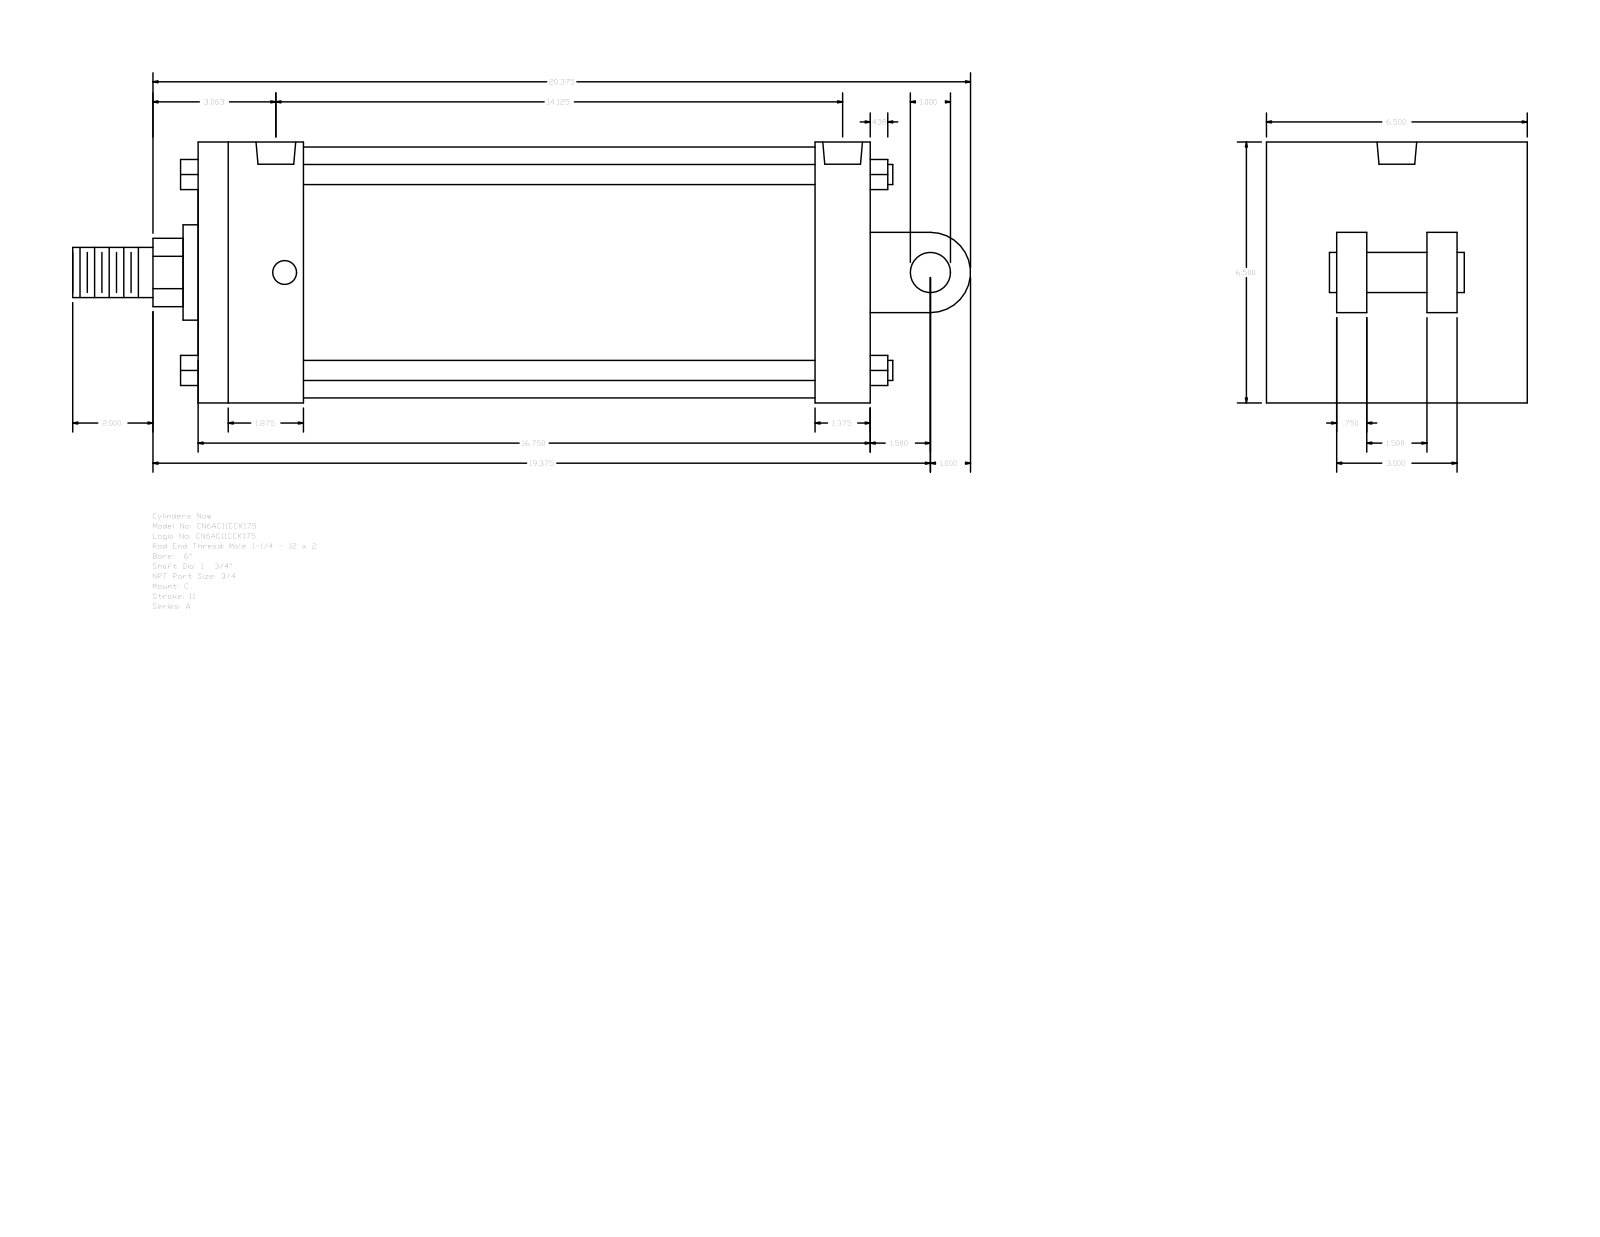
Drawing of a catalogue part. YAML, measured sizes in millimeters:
part_name: "A_C__0600_1.75"
step_written_by: "GSSL Pune (CONFIG_CONTROL_DESIGN)"
units: millimeters
bodies: {solids: 0, faces: 135, planar: 102, cylindrical: 33, other: 0}
overall_size: [568.33, 165.1, 165.1]
round_holes:
  - {diameter: 15.08, count: 4}
  - {diameter: 25.12, count: 2}
round_bosses_or_shafts:
  - {diameter: 12.7, count: 4}
  - {diameter: 158.75, count: 1}
  - {diameter: 60.33, count: 1}
  - {diameter: 44.45, count: 1}
  - {diameter: 31.75, count: 1}
  - {diameter: 25.4, count: 1}
partial_cylinders:
  - {radius: 21.63, count: 1}
  - {radius: 25.4, count: 1}
face_to_face_distances: [165.1, 425.45, 19.05, 57.15, 66.68, 358.77, 390.53, 323.85, 34.92, 63.5]
hole_center_spacings: [5.56, 347.65, 353.21, 358.77]
